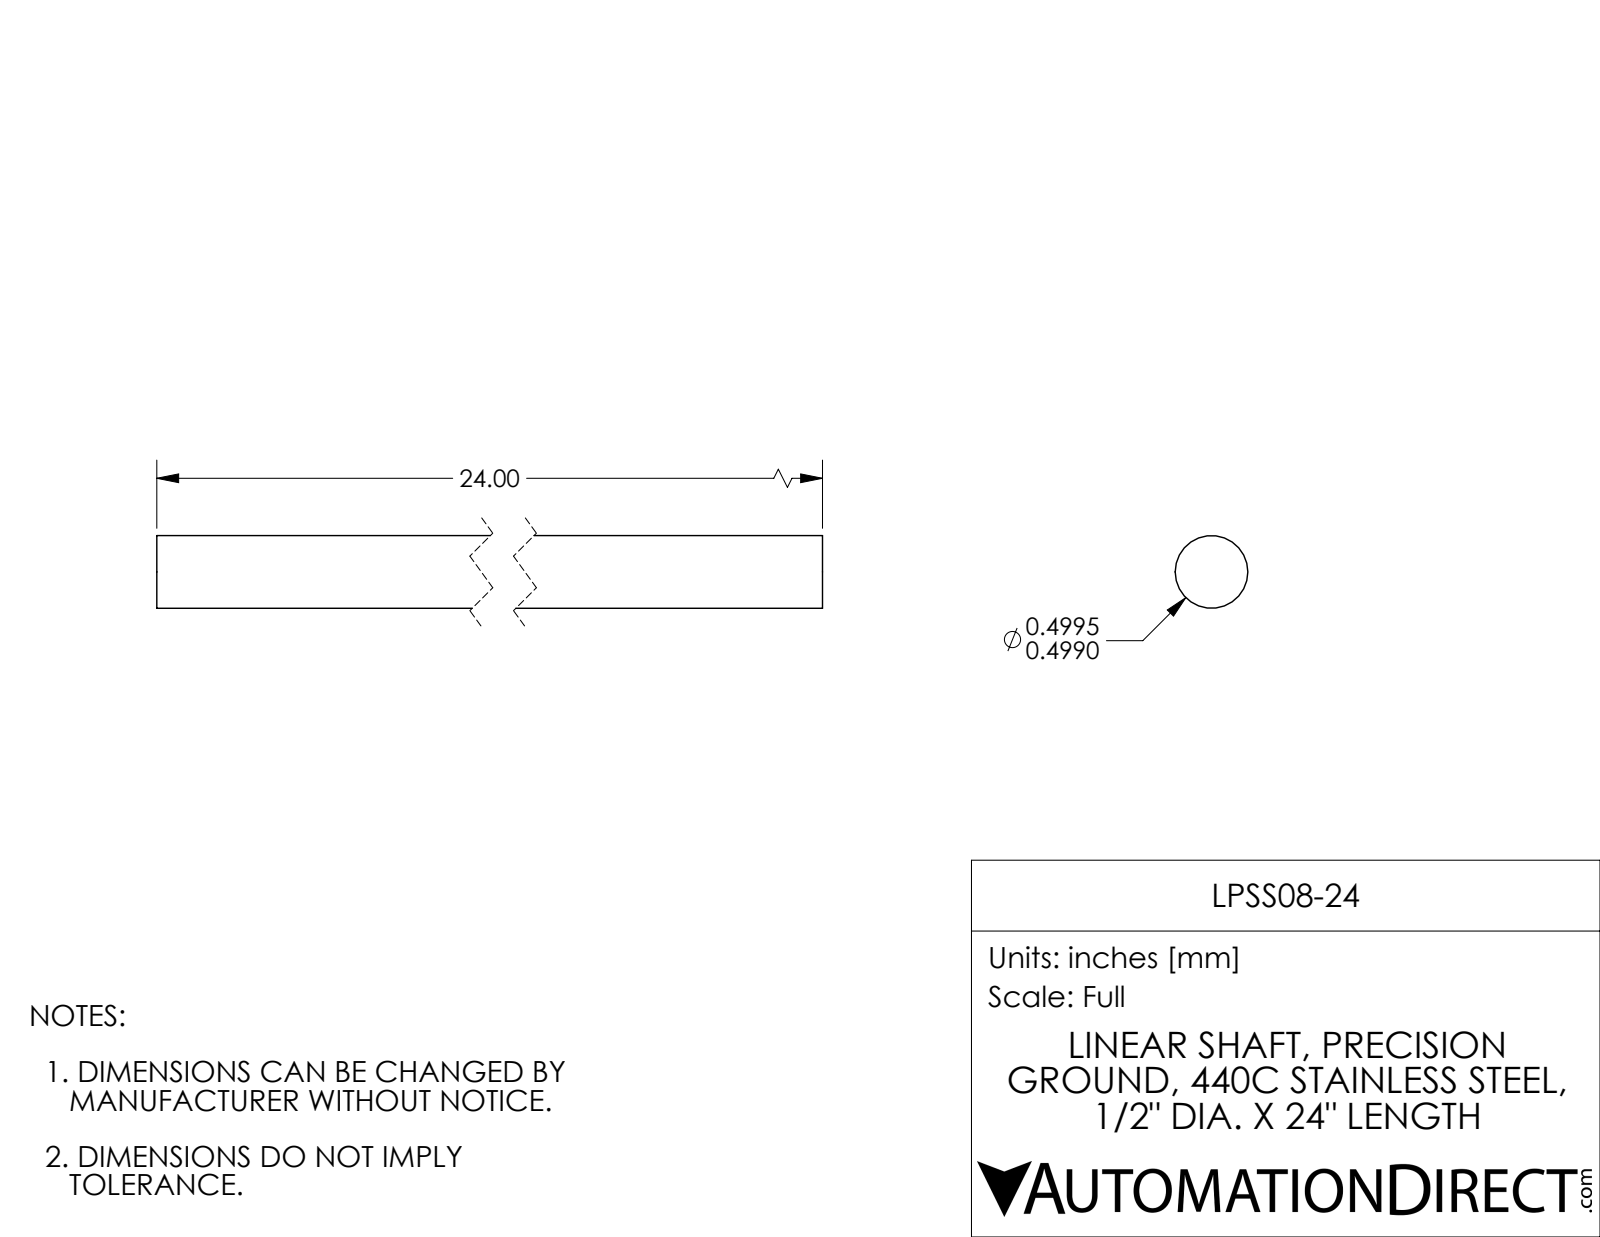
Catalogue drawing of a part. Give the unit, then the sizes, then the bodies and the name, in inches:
Units: inches
Overall size (bounding box): 24 × 0.499 × 0.499
Round bosses / shafts (diameter × count): ⌀0.5 ×1
Main face-to-face distances: 24
Volume: 4.703 in³ · Surface area: 38.05 in²
Bodies: 1 solid, 4 faces (2 planar, 2 cylindrical, 0 other)
Part name (STEP PRODUCT): LPSS08-24
STEP written by: SolidWorks 2017 (AUTOMOTIVE_DESIGN)
